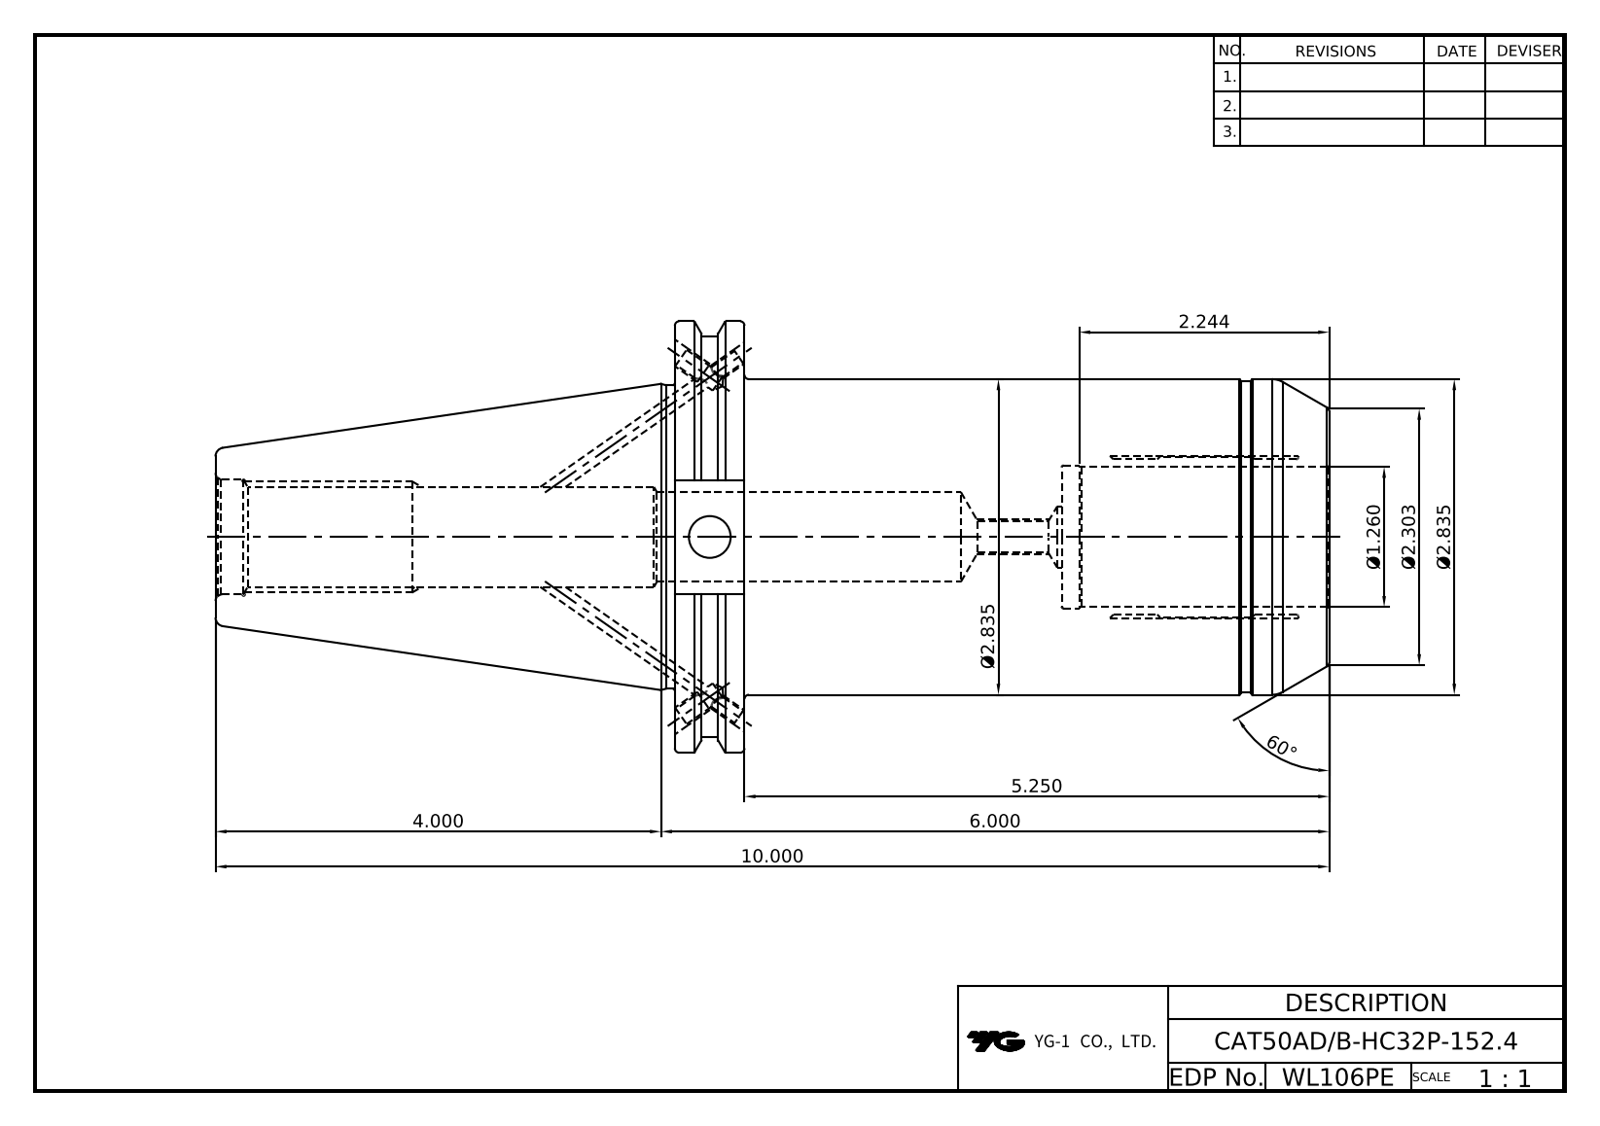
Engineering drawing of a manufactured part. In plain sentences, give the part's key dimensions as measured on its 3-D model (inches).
The part is named "LO-CAT50ADB-HC32P-152.4". Its 3-D file was written by "Autodesk Inventor 2025 (AUTOMOTIVE_DESIGN)". It is 1 solid with 89 faces: 29 planar, 31 cylindrical and 29 other. Overall it measures 10 by 3.875 by 3.728 inches. Its volume is 47.96 cubic inches and its surface area 131.1 square inches. Round holes: 4 of diameter 0.163, 4 of diameter 0.197, 1 of diameter 0.272, 1 of diameter 0.375, 1 of diameter 0.551, 1 of diameter 0.807, 1 of diameter 0.865, 1 of diameter 1.031, 1 of diameter 1.25, 1 of diameter 1.281. Round bosses or shafts: 1 of diameter 3.875, 1 of diameter 3.594, 1 of diameter 2.835, 1 of diameter 2.795, 1 of diameter 2.726. Partial cylindrical surfaces (rounded edges, fillets, slot ends): 1 of radius 0.51. The main face-to-face distances are 0.625, 5.875, 5.25, 3.474, 2.848, 2.402, 4.125, 4.75, 7.598, 10. The hole center spacings are 2.35.
